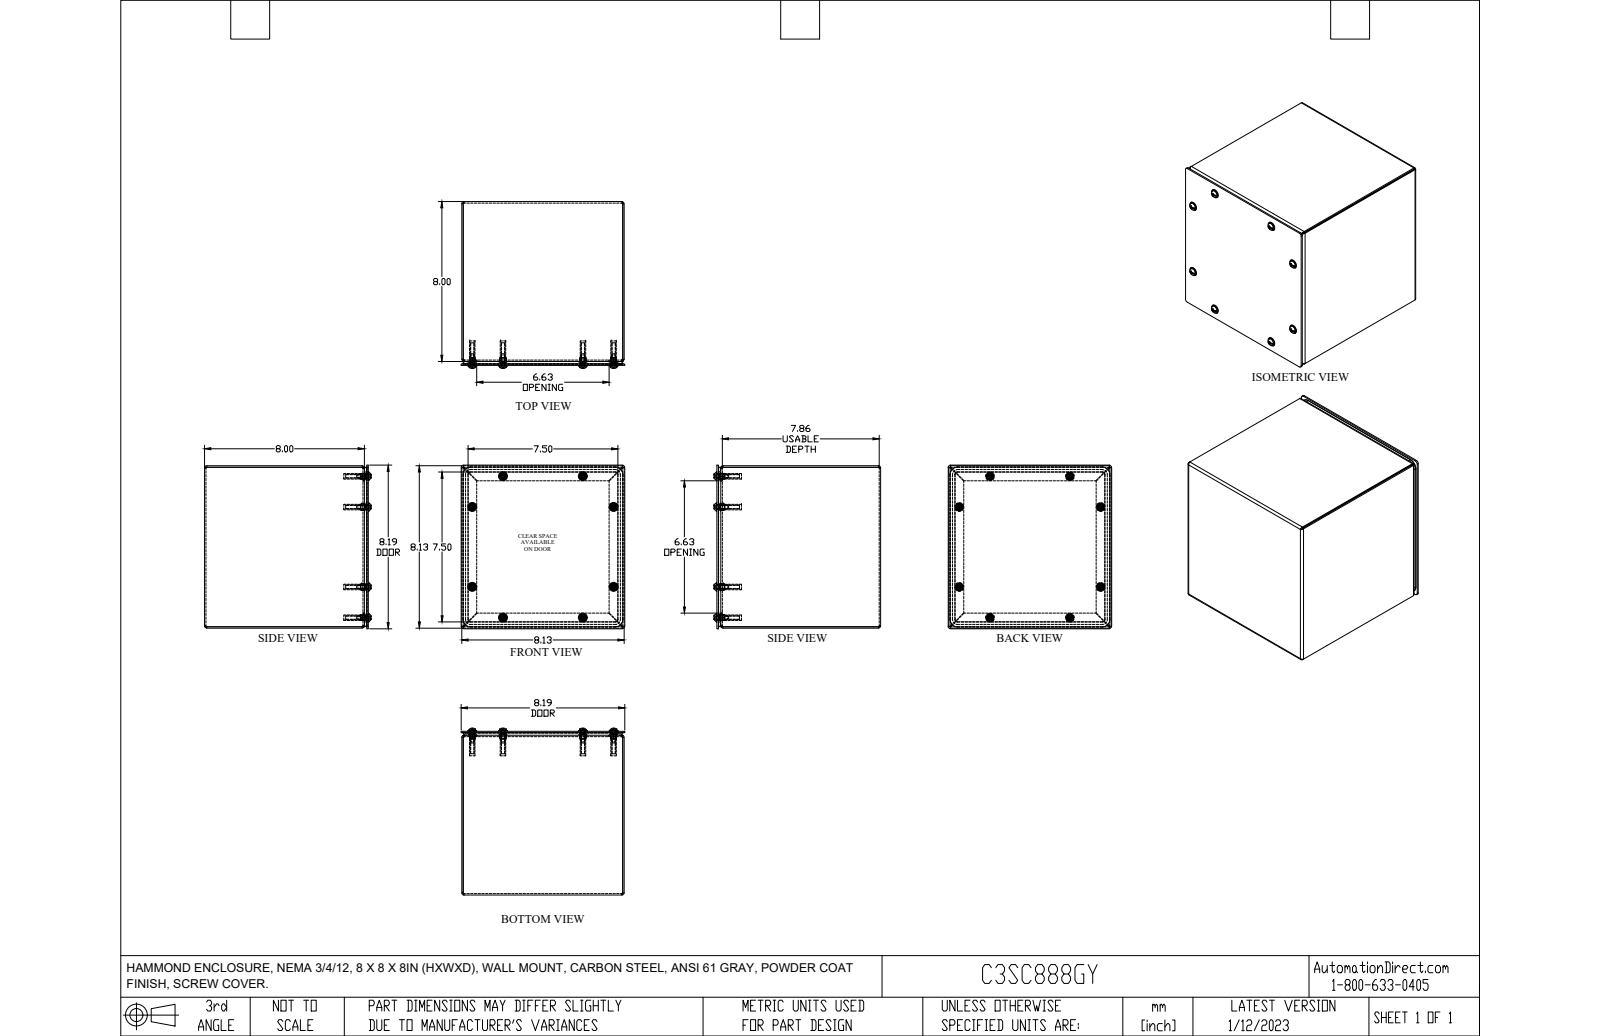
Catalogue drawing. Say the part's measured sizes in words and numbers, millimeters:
The part is named "C3SC888GY". Its 3-D file was written by "SolidWorks 2021 (AUTOMOTIVE_DESIGN)". It is 28 solids with 906 faces: 566 planar, 168 cylindrical and 172 other. Overall it measures 212 by 208 by 208 millimeters. Its volume is 885 100 cubic millimeters and its surface area 1 003 000 square millimeters. Round holes: 8 of diameter 4, 8 of diameter 4.1, 8 of diameter 6.4. Round bosses or shafts: 8 of diameter 11.2, 8 of diameter 9.9, 8 of diameter 6.1, 8 of diameter 4.8, 8 of diameter 3.8, 4 of diameter 7, 4 of diameter 7. Partial cylindrical surfaces (rounded edges, fillets, slot ends): 8 of radius 0.9, 8 of radius 1, 8 of radius 2.7, 8 of radius 2.8, 8 of radius 3.2, 8 of radius 4.1, 4 of radius 3.2, 4 of radius 9.5. The main face-to-face distances are 1.8, 204.5, 1.8, 206.4, 204.6, 206.5, 2, 204.7, 202.7, 202.8. The hole center spacings are 146, 55.2, 101.6, 179.7, 198.9, 206.4.
